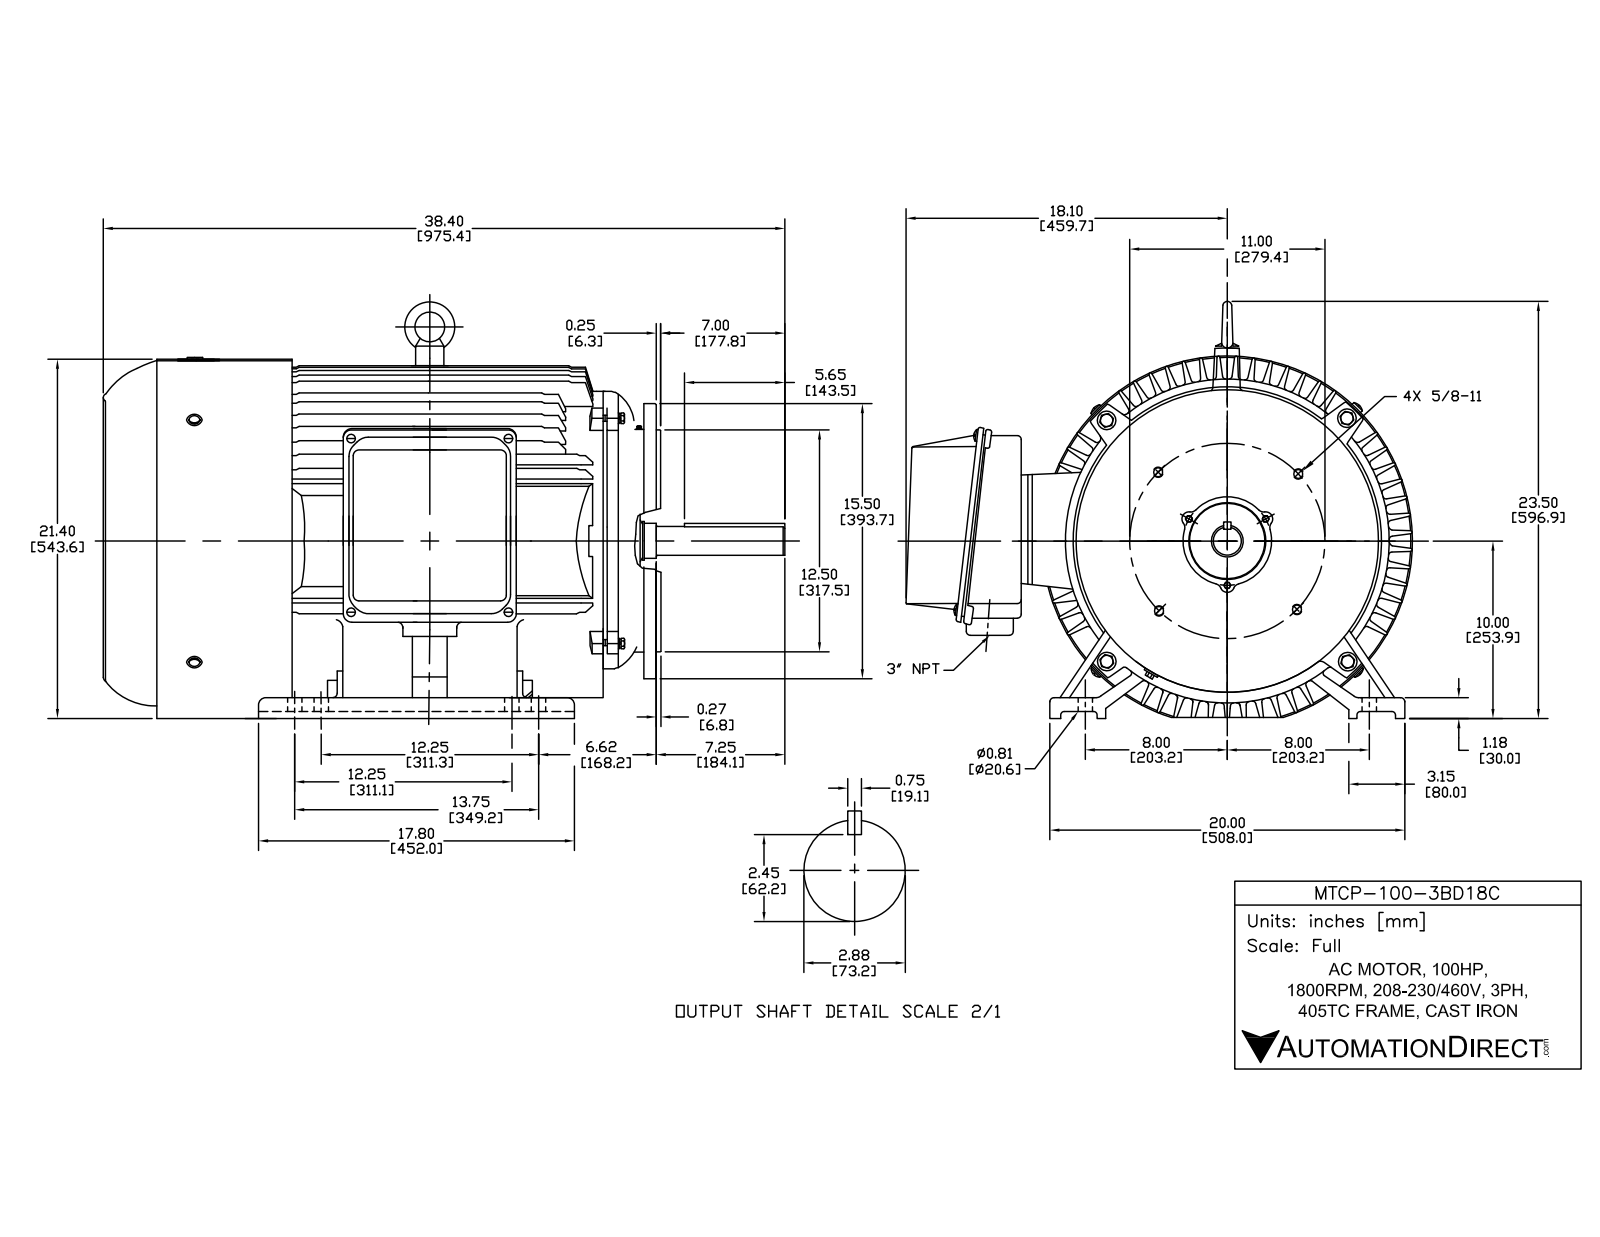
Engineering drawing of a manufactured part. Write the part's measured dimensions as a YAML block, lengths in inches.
part_name: "hexagon head bolts-full thread gb_GB_FASTENER_BOLT_STBAB A M12X65-N; 30橡皮塞; PE400-4,6,8前轴承外盖加工件; plain washers-chamfered--normal series-a gb_GB_FASTENER_WASHER_SWCA 12 (+8 more)"
step_written_by: "SolidWorks 2017 (AUTOMOTIVE_DESIGN)"
units: inches
bodies: {solids: 68, faces: 3874, planar: 962, cylindrical: 1452, other: 1460}
overall_size: [38.469, 29.137, 23.717]
volume: 1797
surface_area: 9348
round_holes:
  - {diameter: 0.394, count: 14}
  - {diameter: 0.472, count: 10}
  - {diameter: 0.268, count: 8}
  - {diameter: 0.531, count: 8}
  - {diameter: 0.827, count: 8}
  - {diameter: 0.098, count: 4}
  - {diameter: 0.276, count: 4}
  - {diameter: 0.331, count: 4}
  - {diameter: 0.335, count: 4}
  - {diameter: 0.342, count: 4}
  - {diameter: 0.354, count: 4}
  - {diameter: 0.402, count: 4}
round_bosses_or_shafts:
  - {diameter: 0.315, count: 12}
  - {diameter: 0.394, count: 7}
  - {diameter: 0.945, count: 4}
  - {diameter: 0.752, count: 4}
  - {diameter: 0.63, count: 4}
  - {diameter: 0.507, count: 4}
  - {diameter: 0.472, count: 4}
  - {diameter: 21.535, count: 1}
partial_cylinders:
  - {radius: 0.039, count: 194}
  - {radius: 0.02, count: 106}
  - {radius: 0.118, count: 84}
  - {radius: 0.197, count: 57}
  - {radius: 0.059, count: 41}
  - {radius: 0.236, count: 32}
  - {radius: 0.157, count: 20}
  - {radius: 0.315, count: 17}
face_to_face_distances: [0.236, 0.079, 5.575, 5.496, 31.165, 31.087, 25.591, 0.157, 4.587, 0.394]
hole_center_spacings: [5.118, 4.209, 5.5, 7.111, 10.163, 11.275, 14.272, 3.445]
